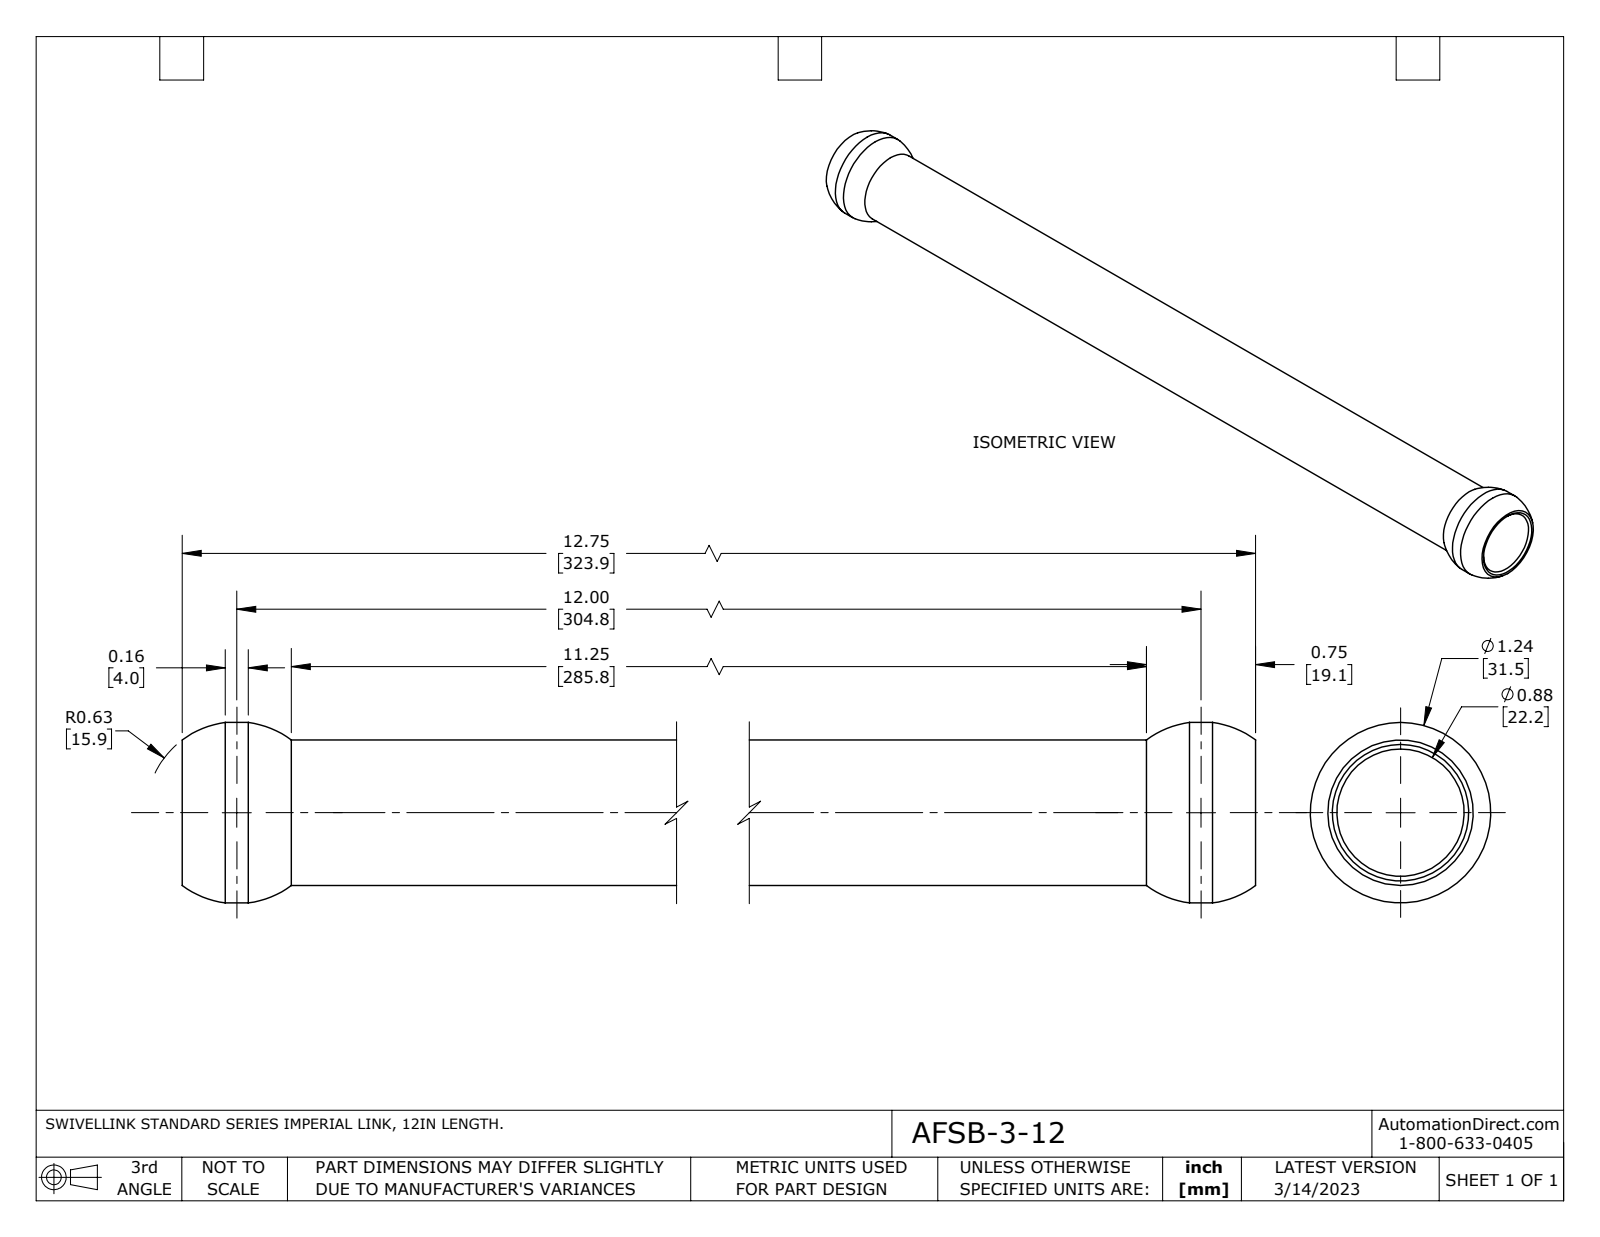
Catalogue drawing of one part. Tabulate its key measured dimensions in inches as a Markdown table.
| quantity | value |
| --- | --- |
| part name | AFSB-3-12 |
| STEP written by | SolidWorks 2021 (AUTOMOTIVE_DESIGN) |
| units | inches |
| bodies | 1 solid, 12 faces (2 planar, 4 cylindrical, 6 other) |
| overall size | 12.75 × 1.24 × 1.24 |
| volume | 2.778 in³ |
| surface area | 76.52 in² |
| round holes (diameter × count) | 0.875 × 1 |
| round bosses / shafts (diameter × count) | 1.24 × 1, 1 × 1 |
| main face-to-face distances | 12.75 |
